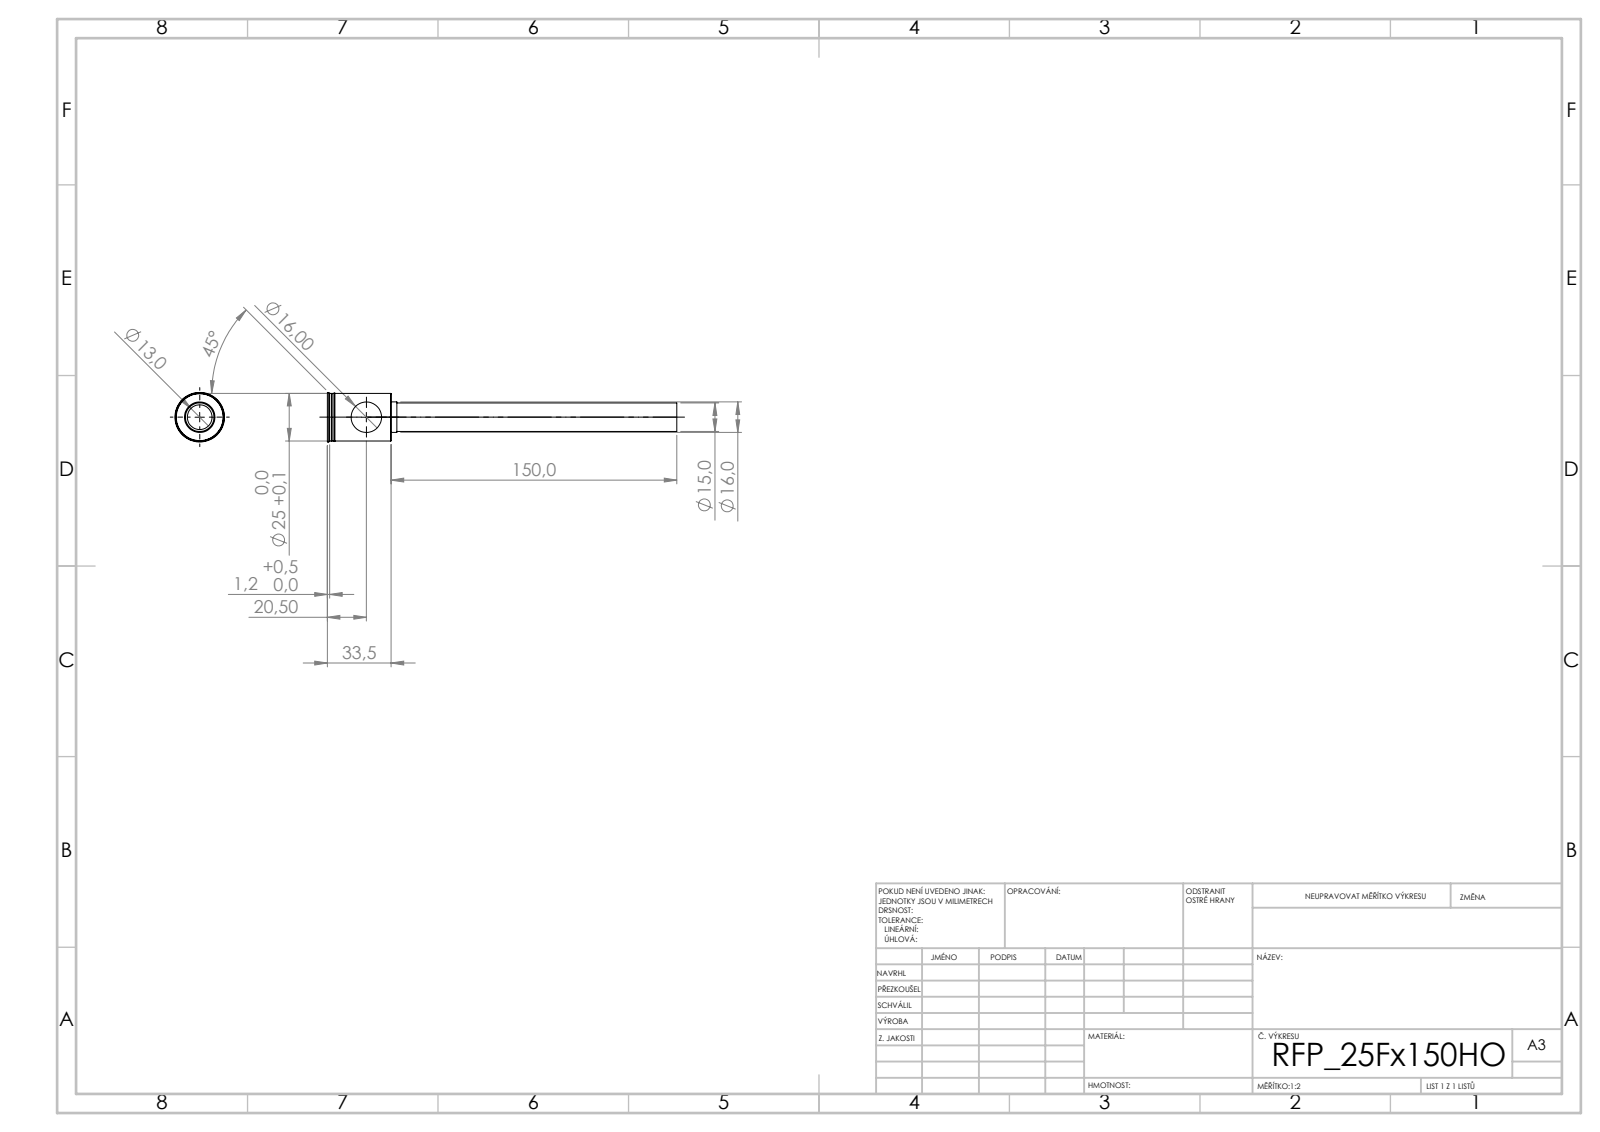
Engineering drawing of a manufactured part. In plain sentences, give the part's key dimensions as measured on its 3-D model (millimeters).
Its 3-D file was written by "SolidWorks 2019 (CONFIG_CONTROL_DESIGN)". It is 1 solid with 44 faces: 20 planar, 16 cylindrical and 8 other. Overall it measures 183.5 by 26 by 26 millimeters. Its volume is 16 920 cubic millimeters and its surface area 17 741 square millimeters. Round holes: 1 of diameter 13, 1 of diameter 16. Round bosses or shafts: 1 of diameter 26, 1 of diameter 25, 1 of diameter 16, 1 of diameter 15. The main face-to-face distances are 31.5, 2, 33.5, 20.4, 150, 181.5, 183.5, 0.5, 147, 3.
